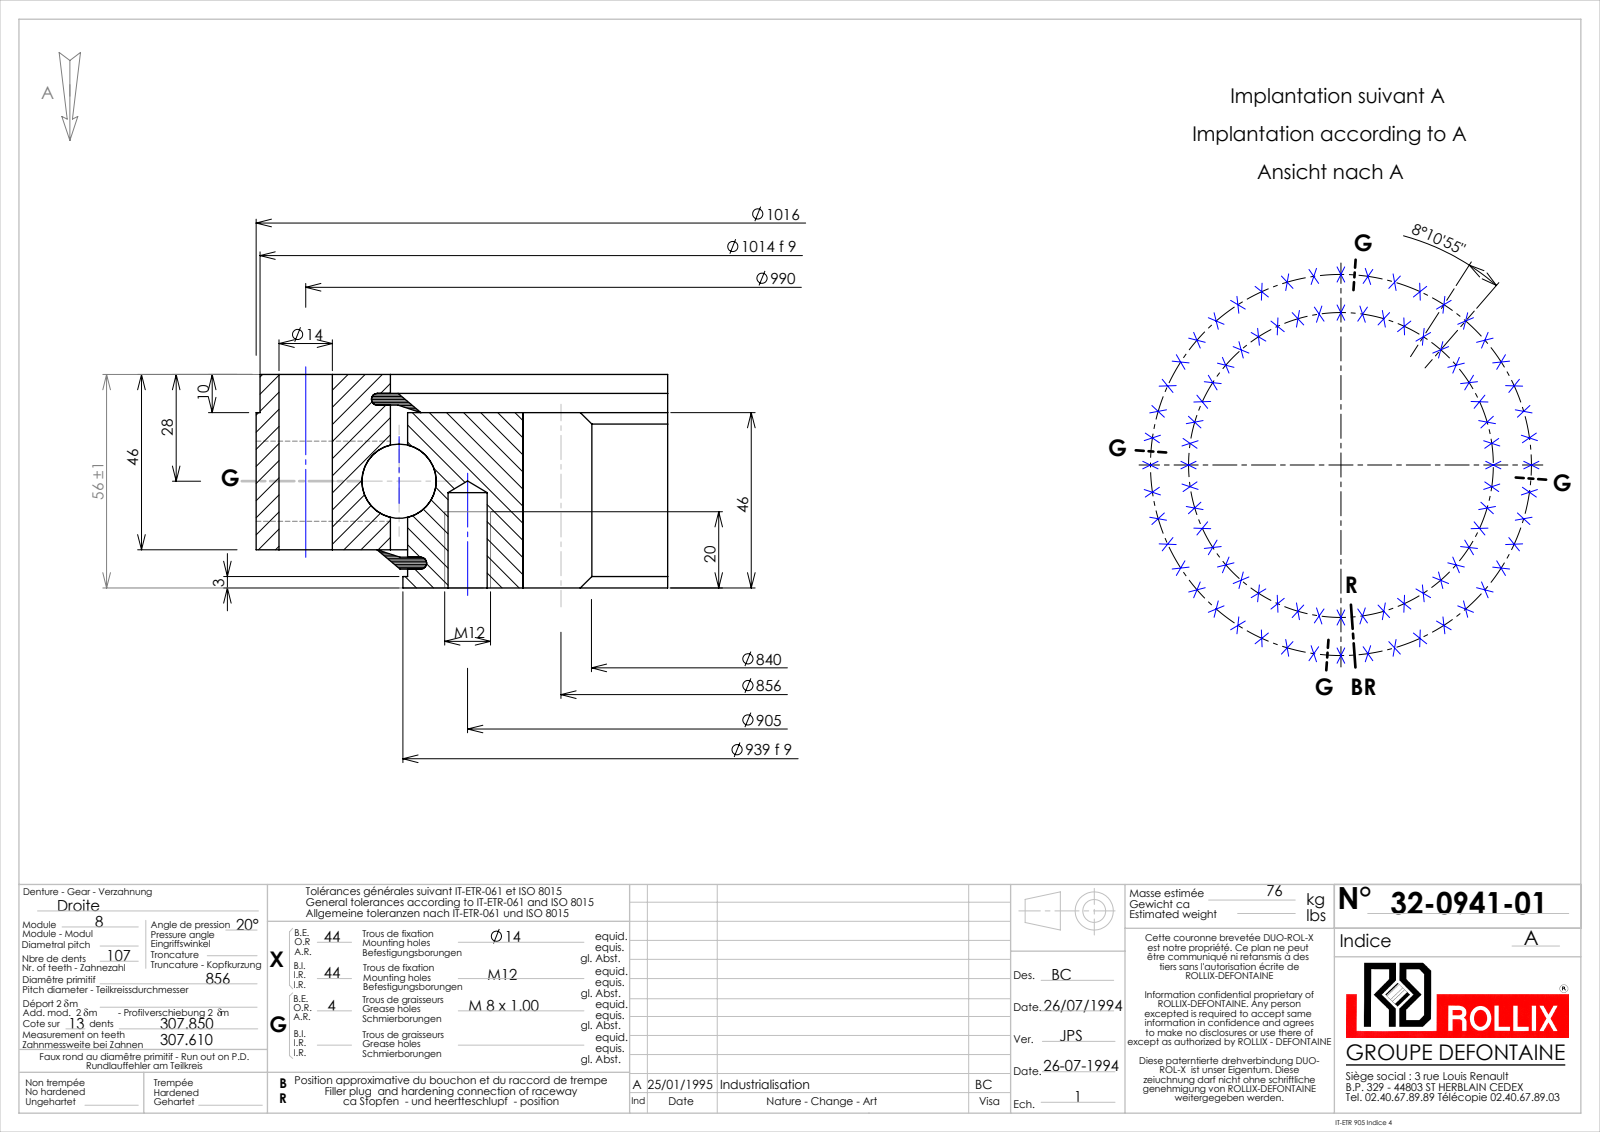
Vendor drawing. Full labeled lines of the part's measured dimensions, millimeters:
Part name (STEP PRODUCT): 32-0941-01
STEP written by: SolidWorks 2016 (CONFIG_CONTROL_DESIGN)
Units: millimetres
Bodies: 9 solids, 1064 faces (268 planar, 425 cylindrical, 371 other)
Overall size (bounding box): 1032.97 × 1032.97 × 56
Volume: 9 175 000 mm³ · Surface area: 1 496 000 mm²
Round holes (diameter × count): ⌀10.25 ×44, ⌀14 ×44, ⌀7 ×4, ⌀945.5 ×1
Round bosses / shafts (diameter × count): ⌀8 ×4, ⌀1016 ×1, ⌀1014 ×1, ⌀939 ×1, ⌀936.5 ×1
Partial cylindrical surfaces — rounded edges, fillets, slot ends (radius × count): R420 ×1, R438 ×1
Main face-to-face distances: 46, 10, 36, 56, 5.05, 1.95, 43, 4.95, 51.05, 41.05
Hole centre spacings: 489.28, 192.37, 128.8, 316.27, 375.95, 64.56, 639.93, 895.79
